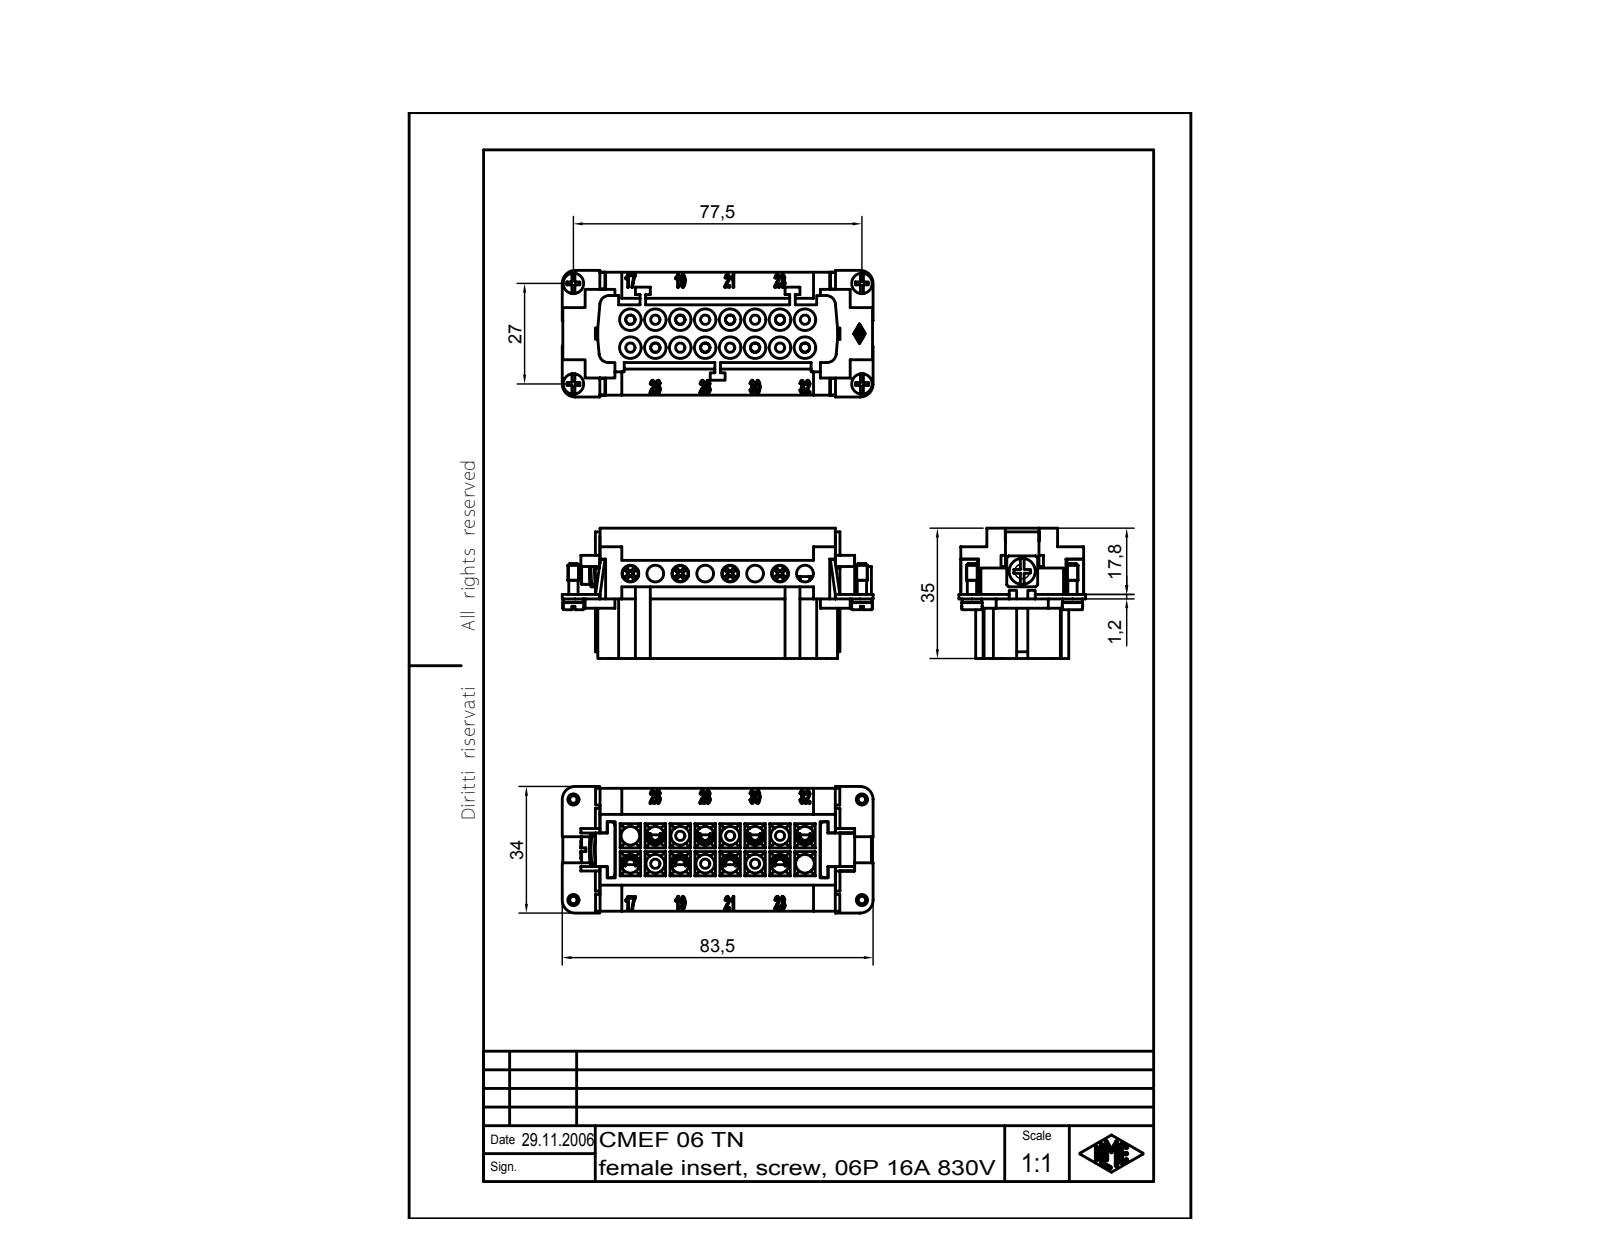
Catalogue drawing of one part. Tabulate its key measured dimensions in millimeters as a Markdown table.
| quantity | value |
| --- | --- |
| part name | CMEF 06 TN |
| STEP written by | Autodesk Inventor 7 (AUTOMOTIVE_DESIGN) |
| units | millimeters |
| bodies | 17 solids, 1582 faces (718 planar, 214 cylindrical, 650 other) |
| overall size | 83.5 × 35 × 34 |
| volume | 39 633 mm³ |
| surface area | 29 671 mm² |
| round holes (diameter × count) | 3 × 8, 4.5 × 8, 5 × 7, 2.55 × 2 |
| round bosses / shafts (diameter × count) | 2.5 × 12, 4.2 × 8, 5.5 × 2, 5.3 × 2, 5 × 2, 3 × 2, 7 × 1 |
| partial cylindrical surfaces (radius × count) | 0.1 × 14, 2.1 × 8, 2.5 × 4, 1 × 2, 3.5 × 2, 1.62 × 1, 5.5 × 1 |
| main face-to-face distances | 1.75, 17.25, 16, 19, 7, 15.5, 8.75, 3.25, 7.1, 24.25 |
| hole center spacings | 13.4, 6.7, 20.1, 26.8, 10.06, 15.36, 21.45, 33.5 |
